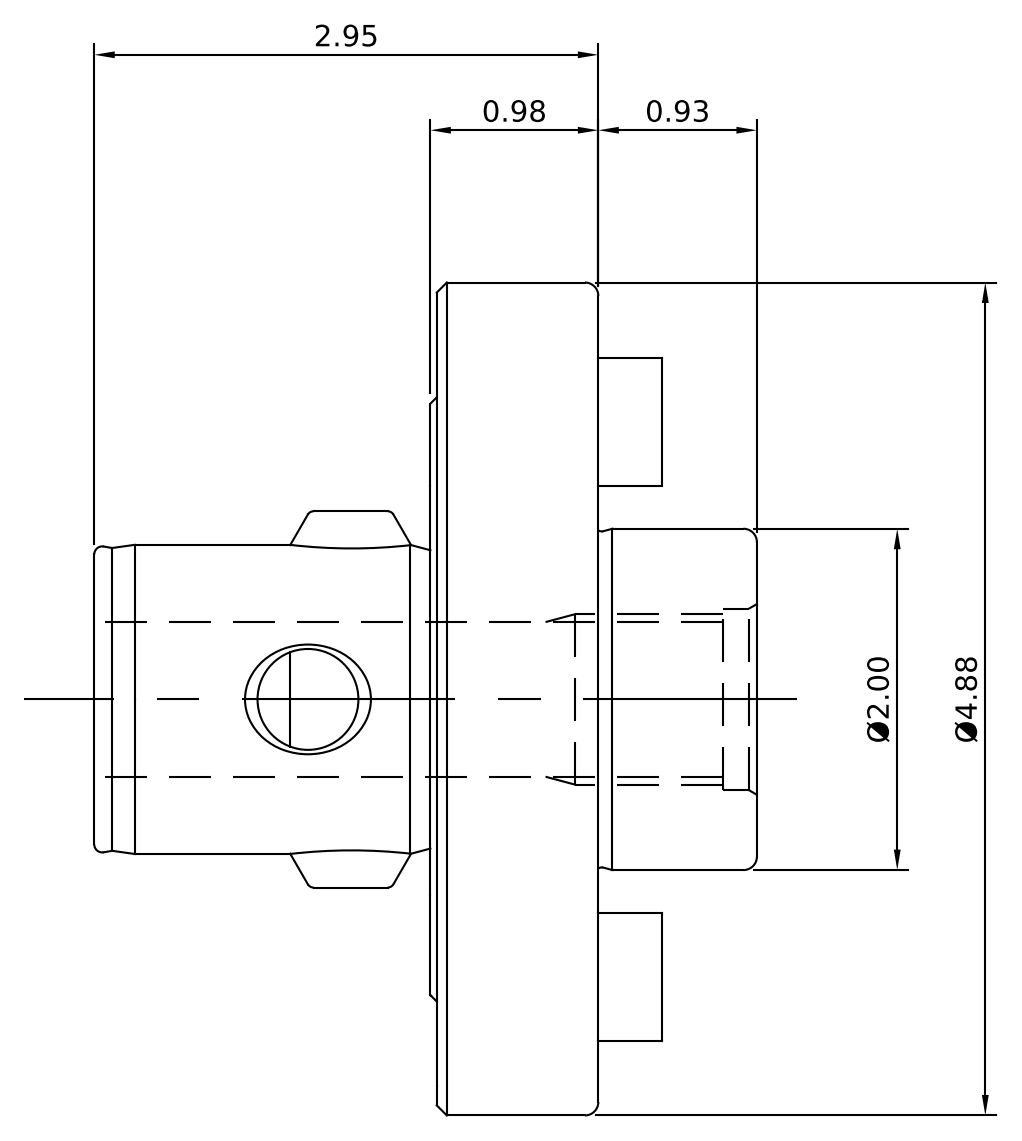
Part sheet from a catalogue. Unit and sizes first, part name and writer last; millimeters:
Units: millimetres
Overall size (bounding box): 123.8 × 123.8 × 98.6
Round holes (diameter × count): ⌀13.49 ×4, ⌀19.05 ×2, ⌀15 ×1, ⌀18 ×1, ⌀22 ×1, ⌀23 ×1, ⌀24.7 ×1, ⌀27 ×1
Round bosses / shafts (diameter × count): ⌀123.8 ×1, ⌀50.79 ×1, ⌀46 ×1, ⌀17.9 ×1, ⌀15.9 ×1, ⌀12 ×1
Partial cylindrical surfaces — rounded edges, fillets, slot ends (radius × count): R23 ×1
Main face-to-face distances: 24, 1, 25, 48.6, 47.6, 23.6, 50, 51, 75, 98.6
Hole centre spacings: 36.32, 50.8, 71.84, 85.14, 41.27, 101.6, 82.54
Volume: 379 925 mm³ · Surface area: 64 495 mm²
Bodies: 5 solids, 155 faces (42 planar, 51 cylindrical, 62 other)
Part name (STEP PRODUCT): 11.335.416; 11.691.625; 10.691.50X_10.691.507; 691-50XRing_10.691.507Ring
STEP written by: SolidWorks 2010 (CONFIG_CONTROL_DESIGN)
